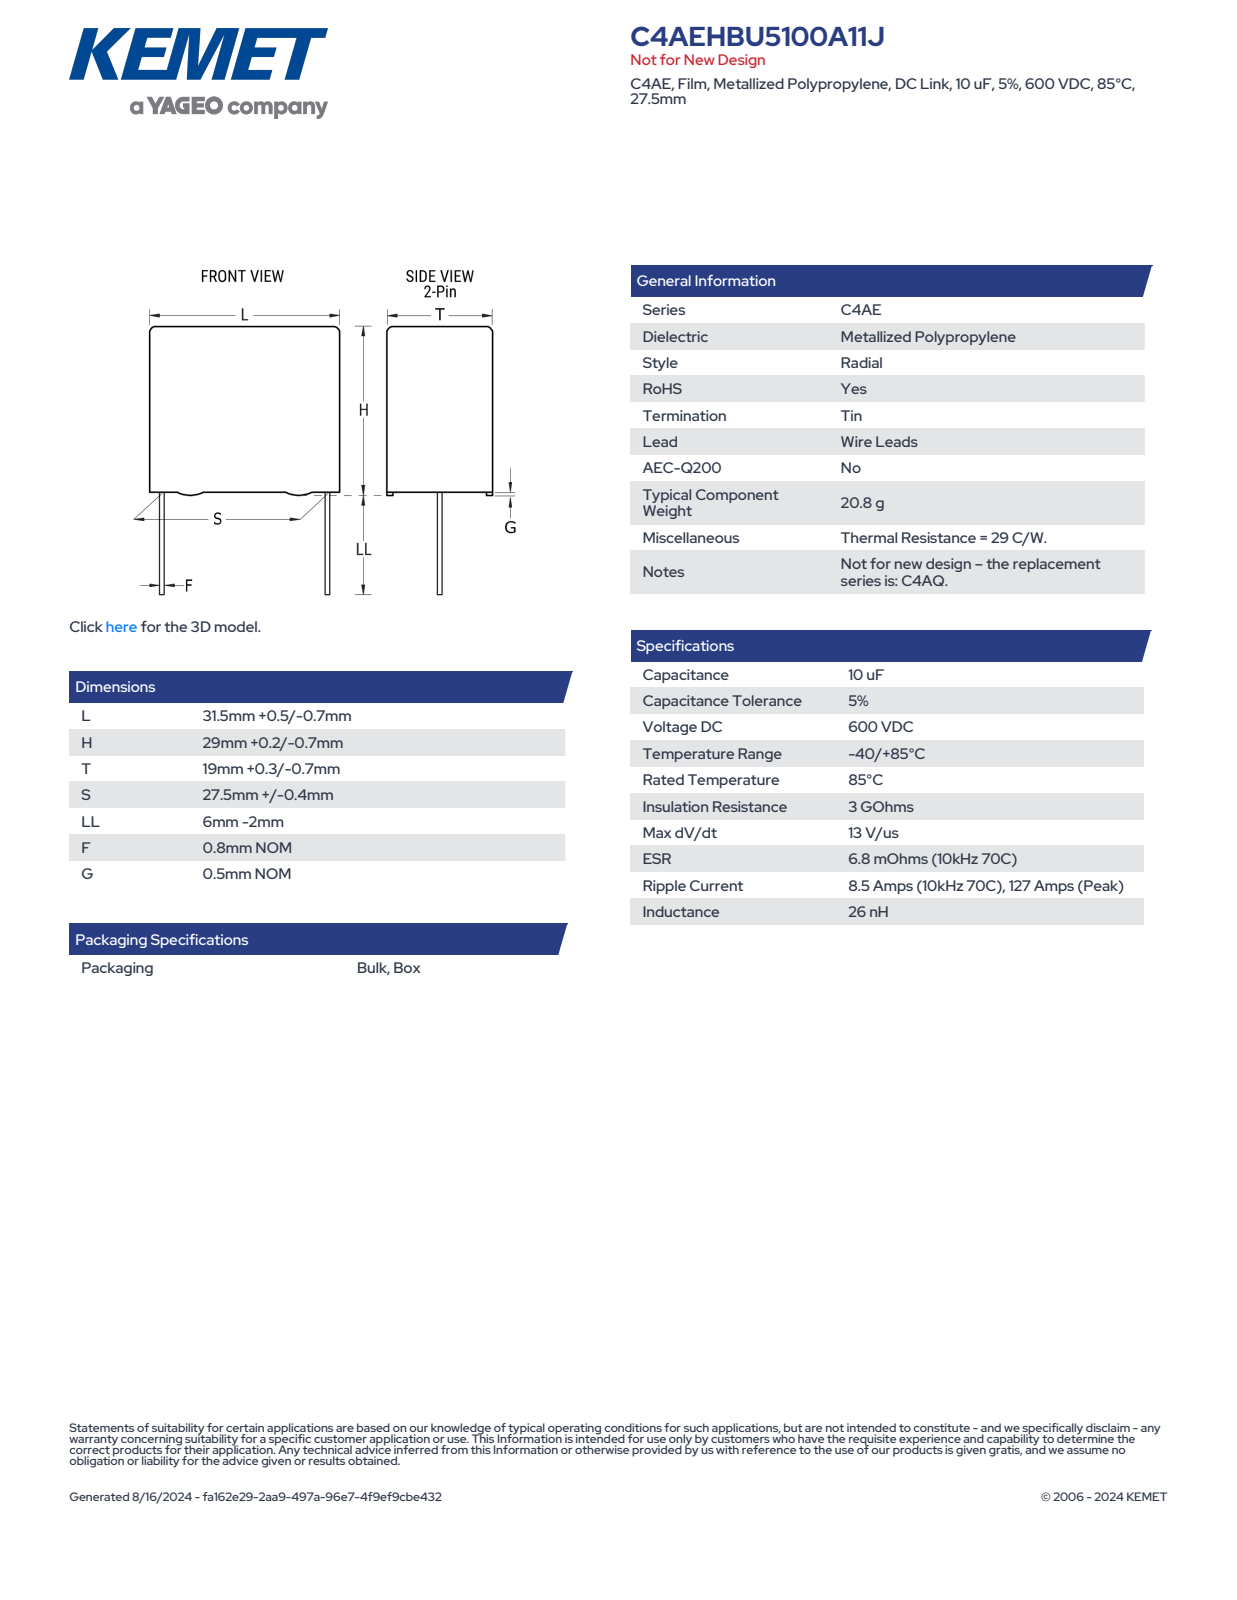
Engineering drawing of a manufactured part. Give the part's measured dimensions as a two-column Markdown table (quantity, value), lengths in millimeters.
| quantity | value |
| --- | --- |
| part name | CFP_RBG_31.5X29X19_L32H29.2T19.3S27.9LL4F0.8G0.5 |
| STEP written by | SolidWorks 2014 (AUTOMOTIVE_DESIGN) |
| units | millimeters |
| bodies | 4 solids, 89 faces (81 planar, 8 cylindrical, 0 other) |
| overall size | 33.2 × 32 × 19.3 |
| volume | 17 742 mm³ |
| surface area | 4 303 mm² |
| round bosses / shafts (diameter × count) | 0.8 × 2 |
| partial cylindrical surfaces (radius × count) | 0.5 × 4 |
| main face-to-face distances | 19.3, 28.7, 32, 0.5, 29.2, 1.71, 17.59, 15.88, 18.78, 4 |
